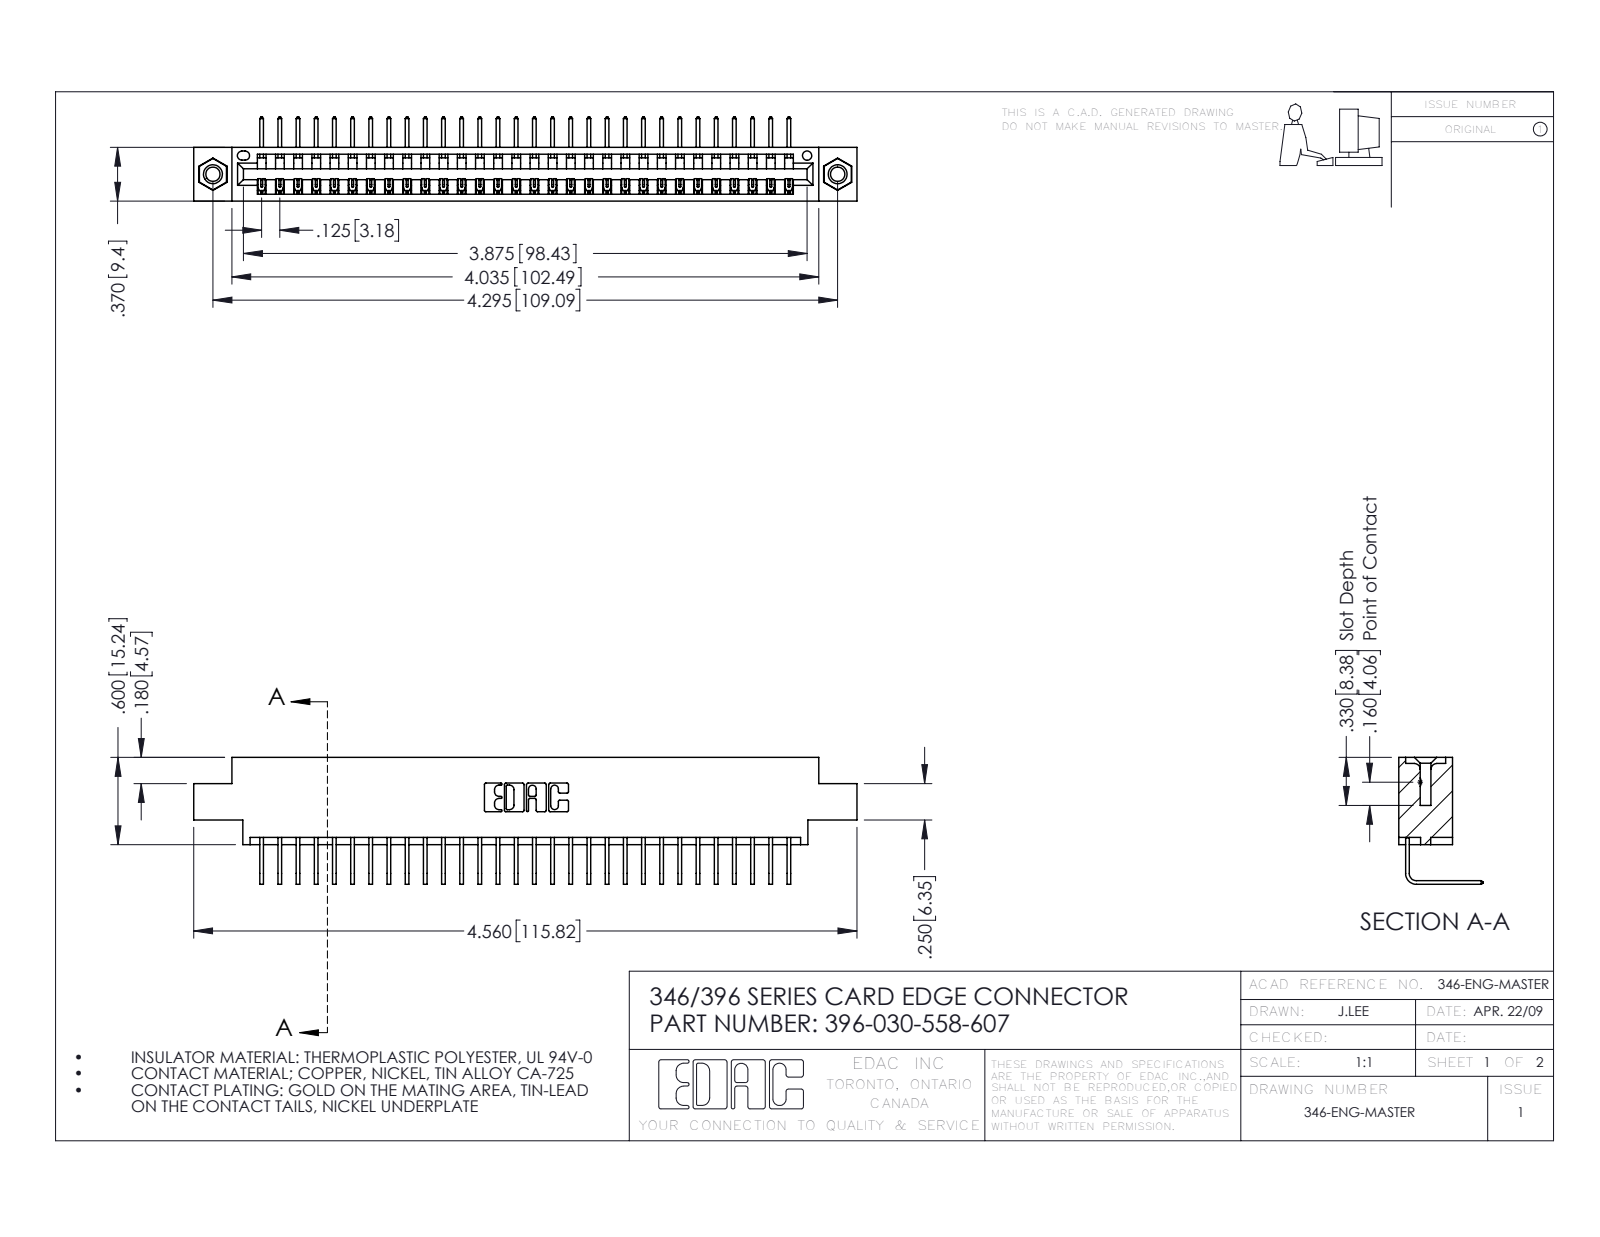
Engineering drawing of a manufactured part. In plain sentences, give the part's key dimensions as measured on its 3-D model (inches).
The part is named "345-250-001_345-250-005-103; 346 Part_0.170 Offset - 0.156 Dia-TI; 345-292-001_558 Tail - 2; 396-030-558-607". Its 3-D file was written by "SolidWorks 2016 (CONFIG_CONTROL_DESIGN)". It is 33 solids with 1986 faces: 1372 planar, 598 cylindrical and 16 other. Overall it measures 4.56 by 0.873 by 0.58 inches. Its volume is 0.667 cubic inches and its surface area 22.21 square inches. Round holes: 2 of diameter 0.098, 2 of diameter 0.125, 2 of diameter 0.156, 1 of diameter 0.064. Round bosses or shafts: 2 of diameter 0.155. Partial cylindrical surfaces (rounded edges, fillets, slot ends): 60 of radius 0.006, 22 of radius 0.01, 6 of radius 0.007, 6 of radius 0.031, 3 of radius 0.026, 2 of radius 0.031, 2 of radius 0.04, 1 of radius 0.014. The main face-to-face distances are 0.322, 0.048, 0.37, 0.25, 0.298, 0.025, 0.072, 0.222, 0.148, 0.1. The hole center spacings are 0.246, 4.087, 4.295.
